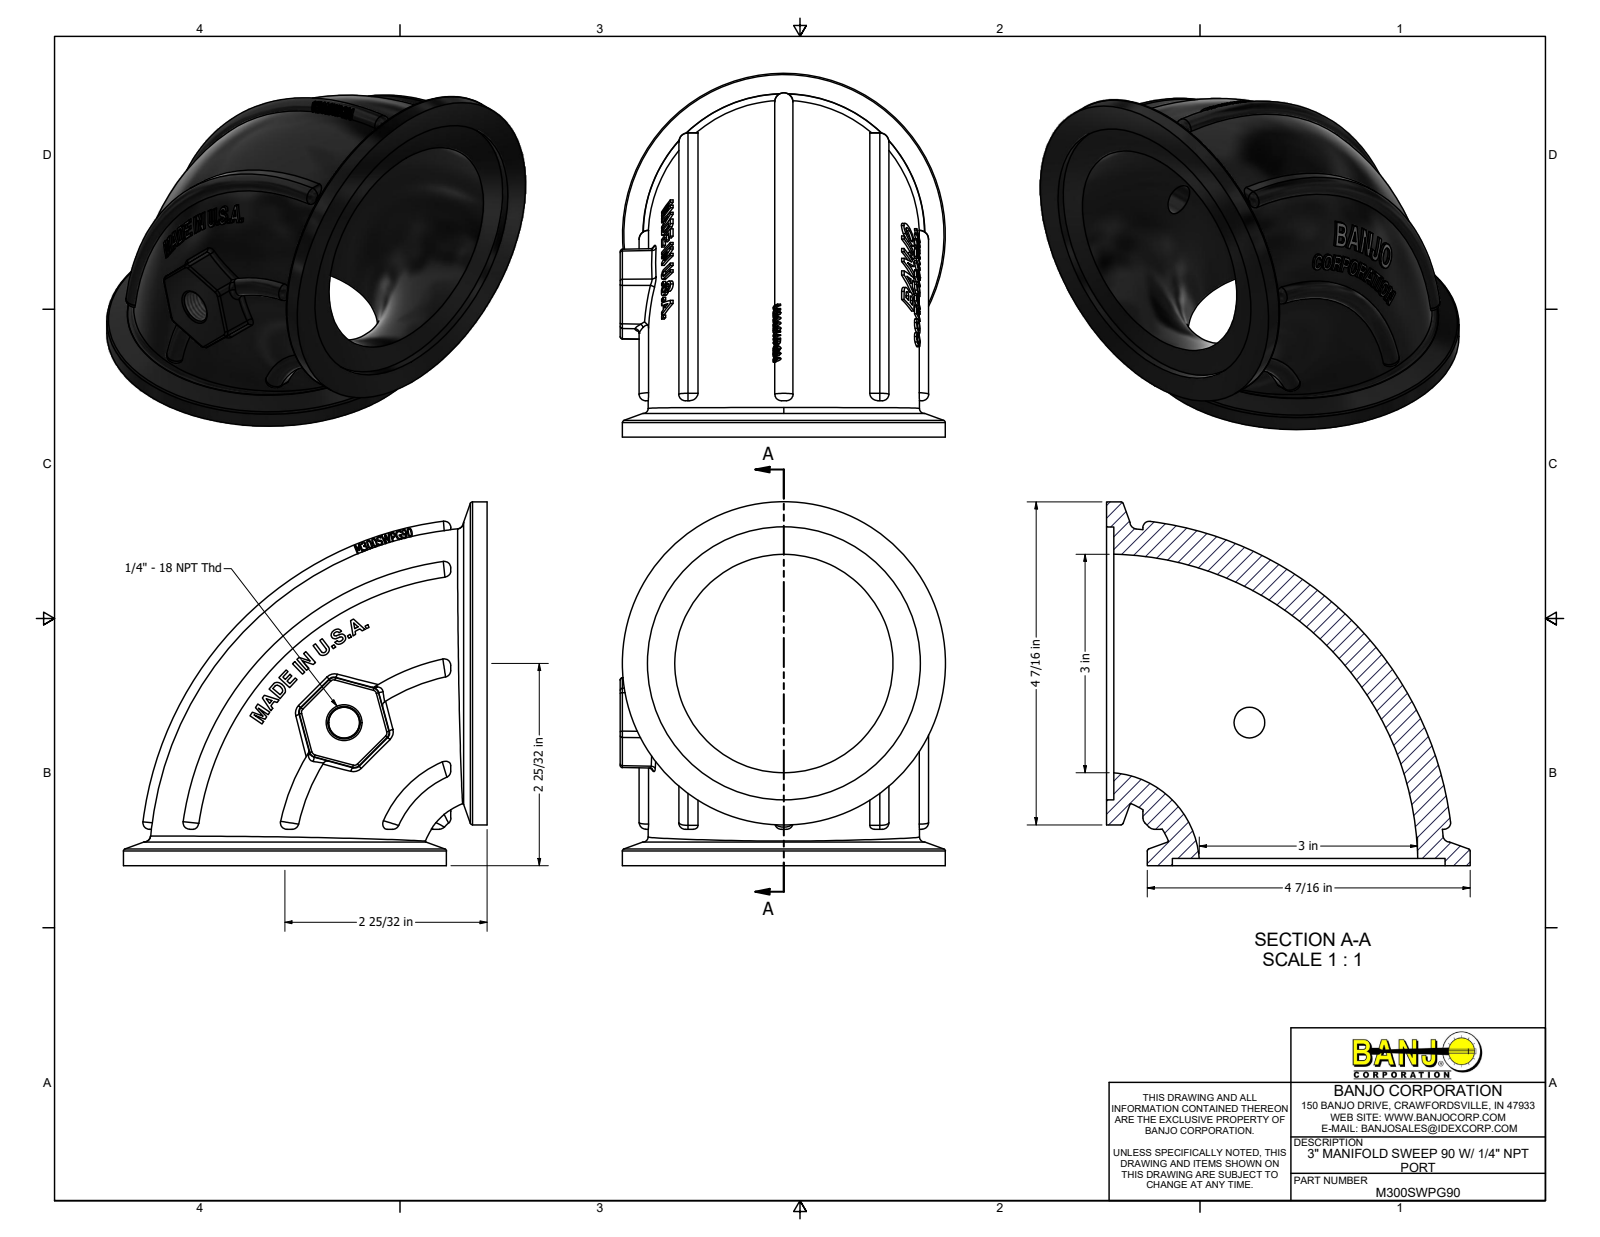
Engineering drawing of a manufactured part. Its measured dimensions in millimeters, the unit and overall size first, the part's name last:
Units: millimetres
Overall size (bounding box): 127 × 127 × 113.5
Round holes (diameter × count): ⌀95.3 ×2, ⌀10.7 ×1
Round bosses / shafts (diameter × count): ⌀112.8 ×2
Partial cylindrical surfaces — rounded edges, fillets, slot ends (radius × count): R2.3 ×10, R0.8 ×6, R33.9 ×1, R107.3 ×1
Main face-to-face distances: 2.5, 8.2, 5.7, 1, 12.7, 10.2, 4.5, 1.6, 1, 5.1
Volume: 322 000 mm³ · Surface area: 79 870 mm²
Bodies: 1 solid, 657 faces (277 planar, 29 cylindrical, 351 other)
Part name (STEP PRODUCT): M300SWPG90; M300SWPG90X
STEP written by: Autodesk Inventor 2019 (AUTOMOTIVE_DESIGN)
